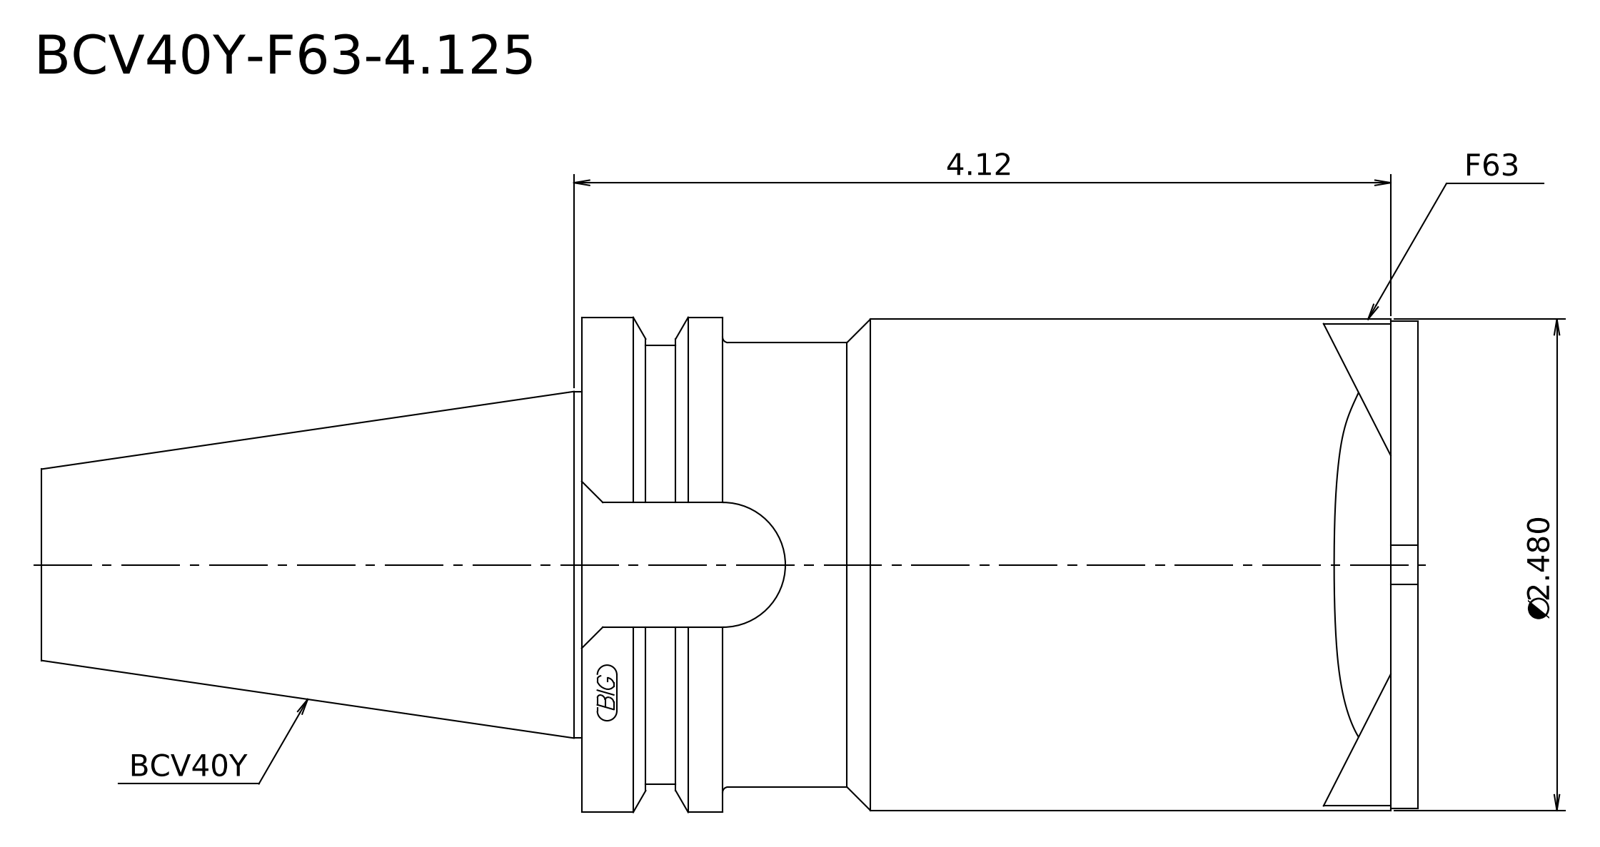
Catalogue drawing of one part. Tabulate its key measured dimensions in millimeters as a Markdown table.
| quantity | value |
| --- | --- |
| STEP written by | Kubotek KeyCreator 2011 V10.0.2 (22737) (automotive_design) |
| units | millimeters |
| bodies | 1 solid, 16 faces (6 planar, 6 cylindrical, 4 other) |
| overall size | 172.95 × 63.5 × 63.5 |
| volume | 377 939 mm³ |
| surface area | 34 675 mm² |
| round bosses / shafts (diameter × count) | 63.5 × 1, 63 × 1, 57 × 1, 56.36 × 1, 44.45 × 1 |
| main face-to-face distances | 103.7, 85.65, 18.05, 172.95, 87.3, 69.25, 91.66, 6.01, 12.04, 81.29 |
